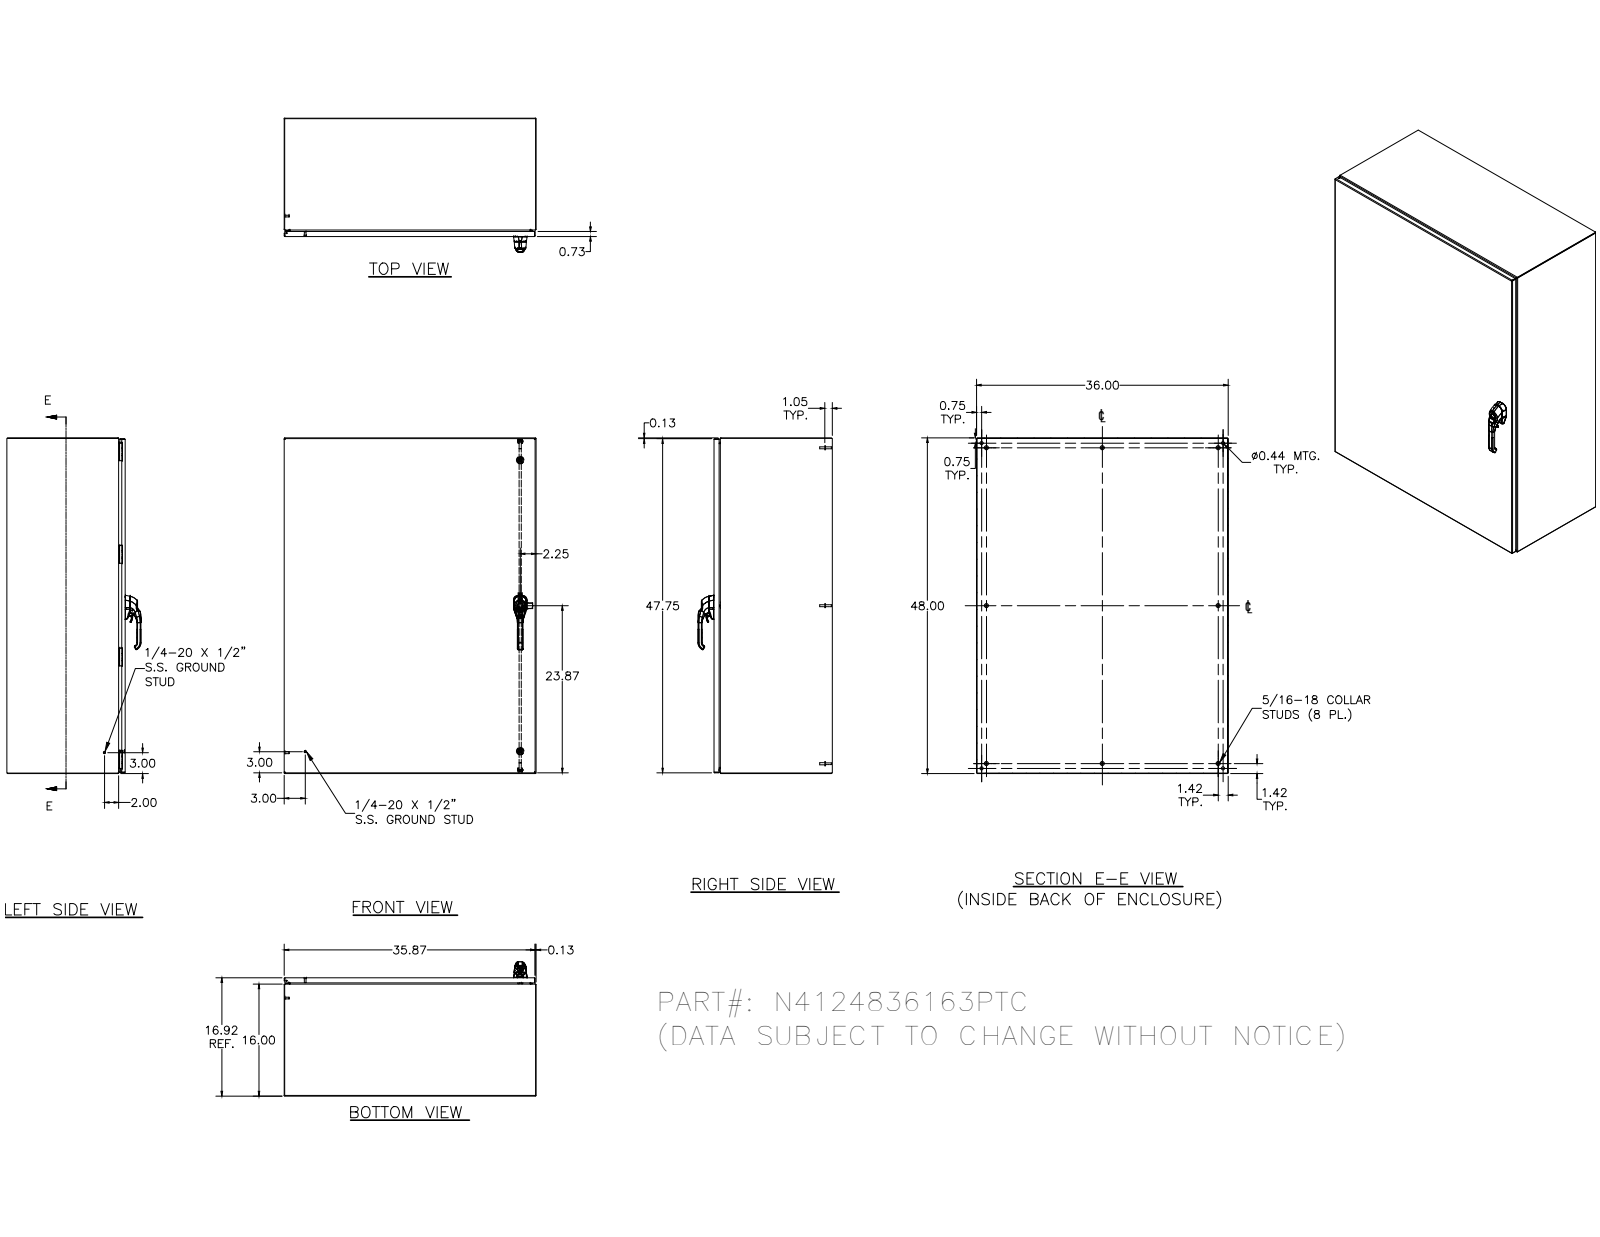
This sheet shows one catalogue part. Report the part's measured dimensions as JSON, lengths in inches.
{"part_name": "N4124836163PTC", "step_written_by": "SolidWorks 2019 (AUTOMOTIVE_DESIGN)", "units": "inches", "bodies": {"solids": 75, "faces": 2490, "planar": 837, "cylindrical": 932, "other": 721}, "overall_size": [48, 36, 19.095], "volume_in3": 494.3, "surface_area_in2": 13119, "round_holes": [[0.188, 9], [0.093, 8], [0.152, 8], [0.167, 8], [0.172, 8], [0.156, 4], [0.165, 4], [0.197, 4], [0.438, 4], [0.106, 2], [0.16, 2], [0.169, 2]], "round_bosses_or_shafts": [[0.25, 18], [0.563, 8], [0.36, 8], [0.32, 8], [0.3, 8], [0.256, 8], [0.164, 8], [0.131, 8]], "partial_cylinders_radius": [[0.05, 50], [0.031, 36], [0.016, 34], [0.125, 28], [0.02, 18], [0.105, 18], [0.032, 16], [0.118, 16]], "face_to_face_distances": [0.074, 16.843, 16.917, 16.769, 35.926, 47.926, 35.852, 36, 47.852, 48], "hole_center_spacings": [14.667, 29.333, 44, 0.66, 0.017, 14.667, 0.5, 0.656]}
